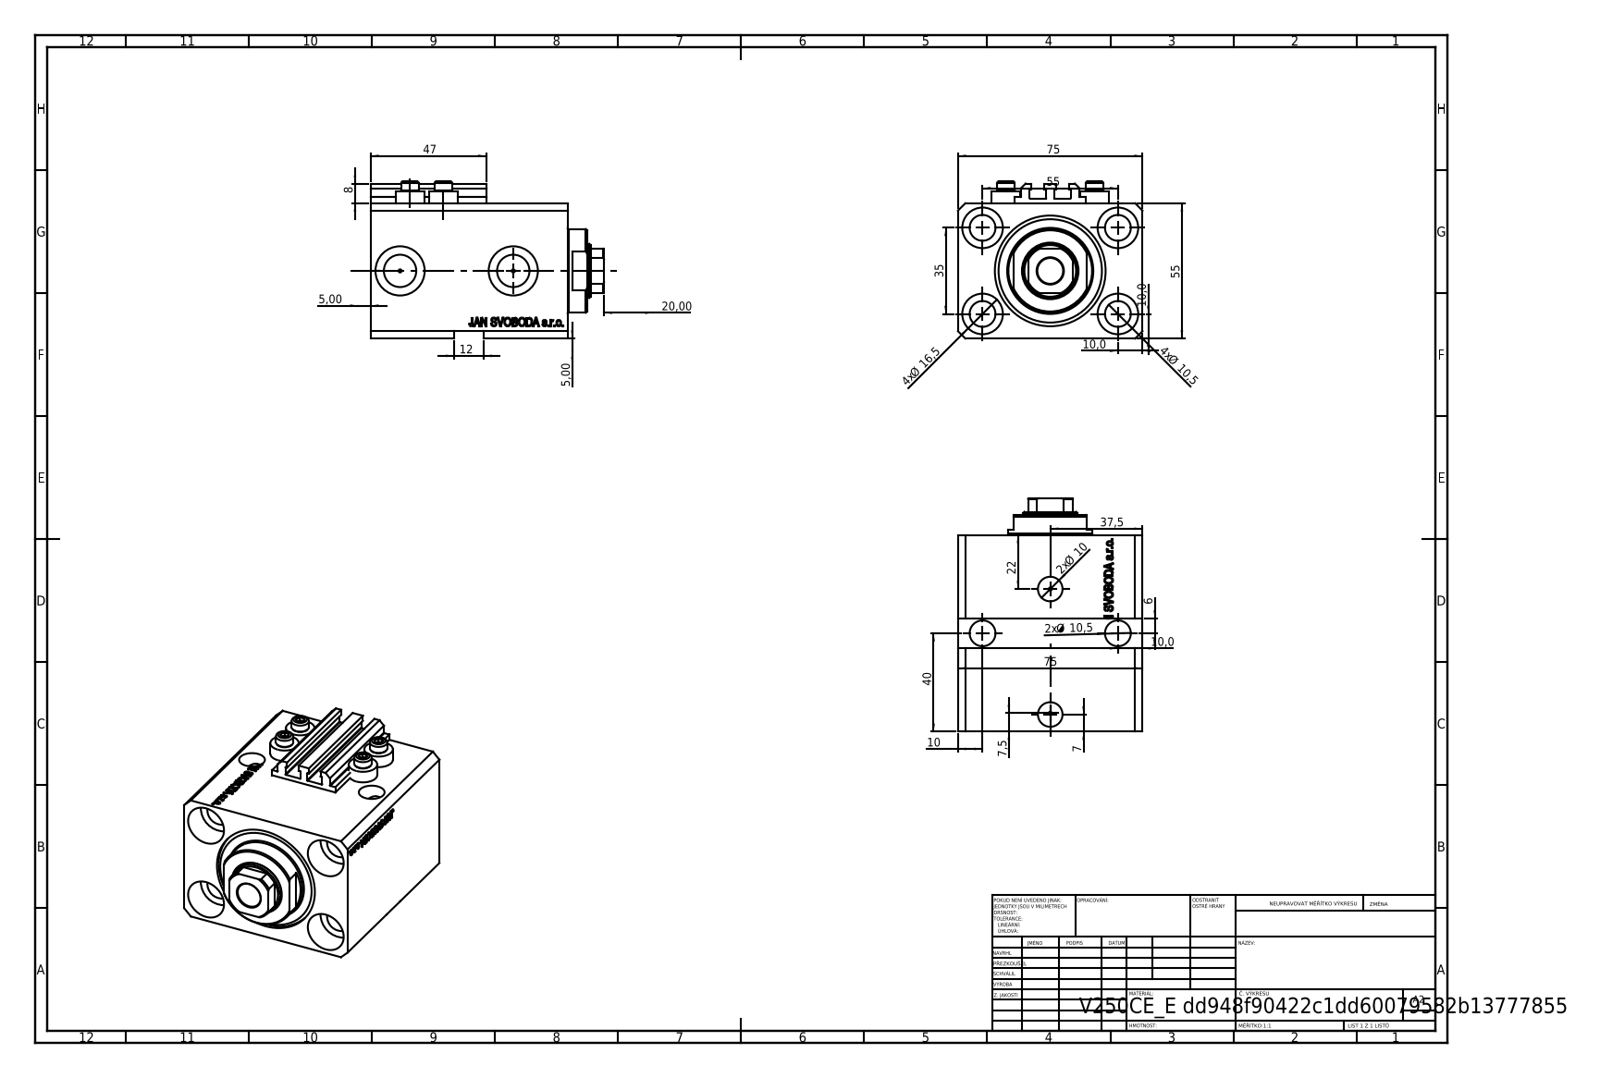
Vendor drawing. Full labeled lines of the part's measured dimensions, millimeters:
Part name (STEP PRODUCT): ALLEN BOLT V250CE; V250CE_E_Body; V250CE_C_VCP; V250CE_VC_E
STEP written by: SolidWorks 2019 (CONFIG_CONTROL_DESIGN)
Units: millimetres
Bodies: 8 solids, 1064 faces (514 planar, 126 cylindrical, 424 other)
Overall size (bounding box): 94.9 × 75 × 64
Volume: 283 872 mm³ · Surface area: 77 066 mm²
Round holes (diameter × count): ⌀10.5 ×7, ⌀1.25 ×4, ⌀4 ×4, ⌀16.5 ×4, ⌀10 ×2, ⌀13.16 ×2, ⌀20 ×2, ⌀22 ×1, ⌀32 ×1, ⌀45 ×1
Round bosses / shafts (diameter × count): ⌀11.6 ×4, ⌀7 ×4, ⌀34 ×1
Partial cylindrical surfaces — rounded edges, fillets, slot ends (radius × count): R0.2 ×10, R10.5 ×1
Main face-to-face distances: 55, 75, 80, 52.9, 27.1, 3, 9.9, 43, 70.1, 23
Hole centre spacings: 32.6, 55, 13.6, 14.09, 19.89, 20.12, 25.81, 28.48
